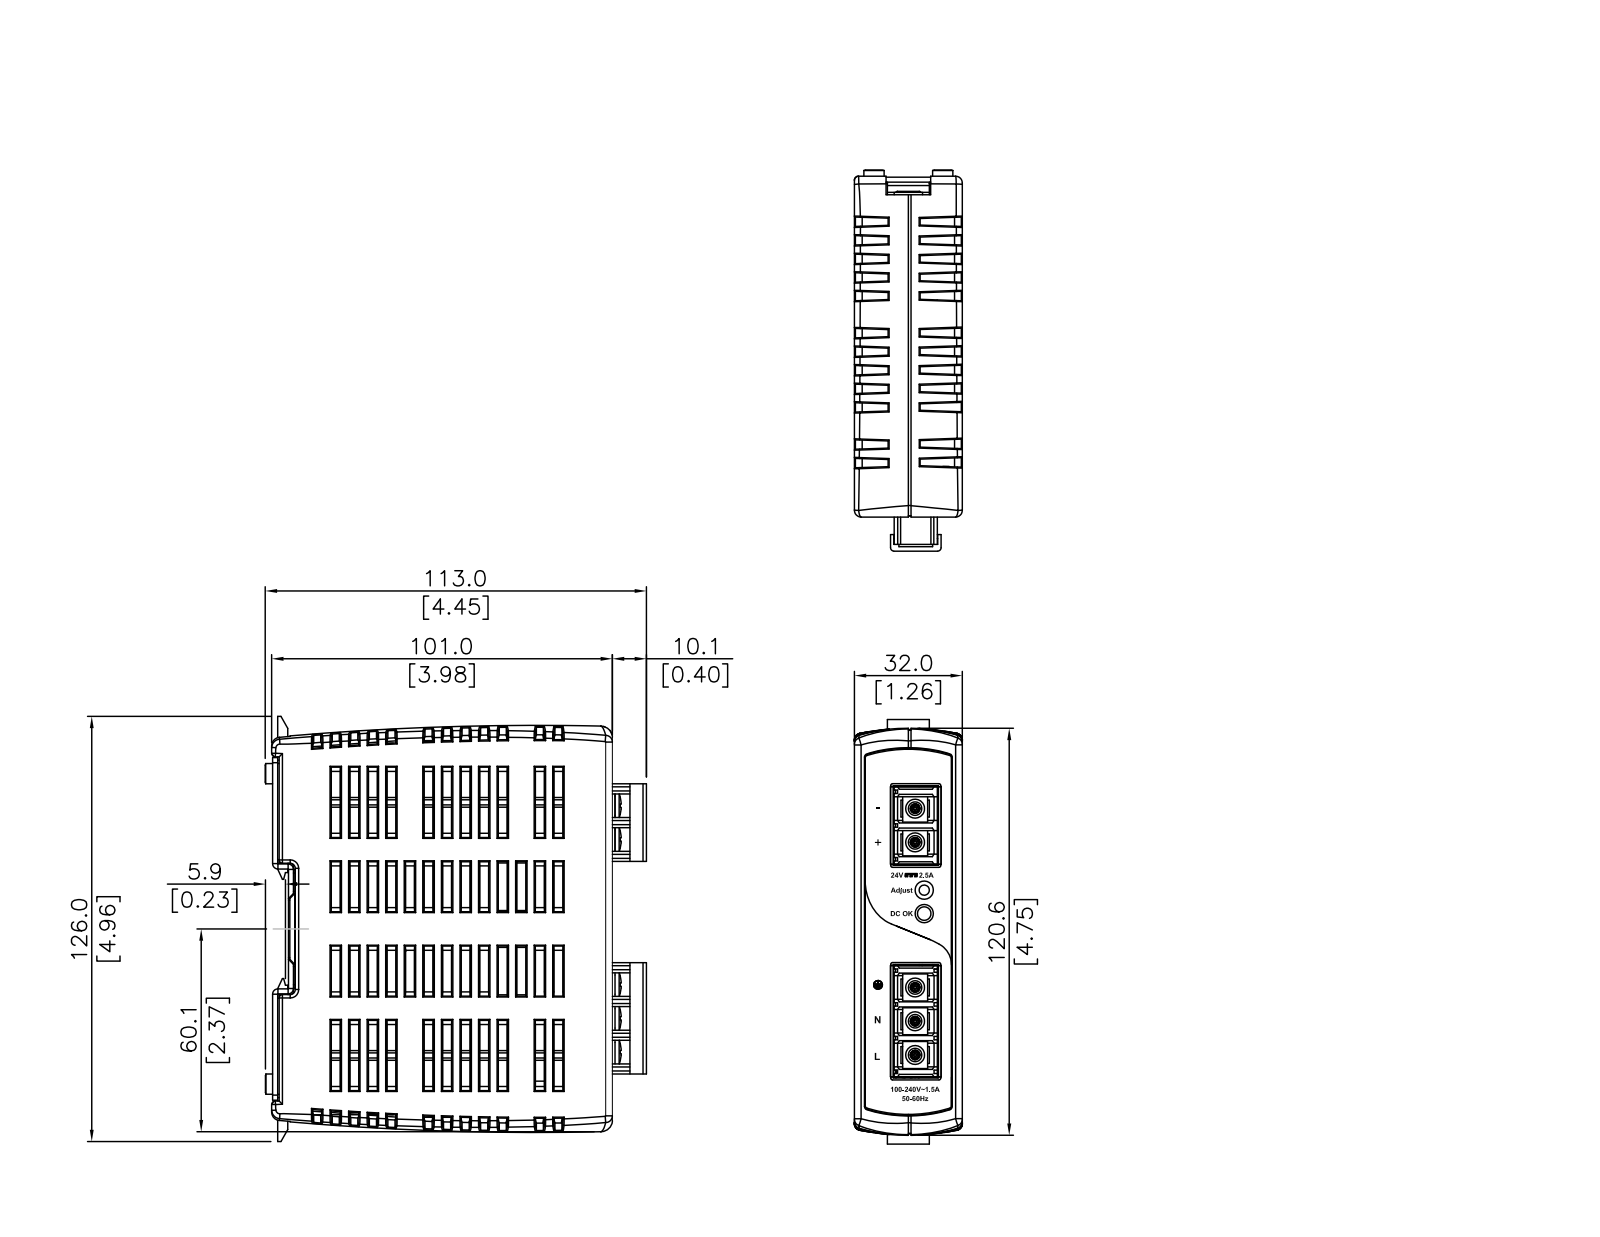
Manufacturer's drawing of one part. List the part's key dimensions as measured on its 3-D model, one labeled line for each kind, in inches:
Part name (STEP PRODUCT): PSB24-060-P.
STEP written by: SolidWorks 2011 (CONFIG_CONTROL_DESIGN)
Units: inches
Bodies: 1 solid, 1354 faces (1032 planar, 74 cylindrical, 248 other)
Overall size (bounding box): 4.98 × 4.398 × 1.26
Volume: 16.01 in³ · Surface area: 120.4 in²
Round holes (diameter × count): ⌀0.175 ×2
Round bosses / shafts (diameter × count): ⌀0.202 ×5, ⌀0.21 ×4, ⌀0.094 ×1
Partial cylindrical surfaces — rounded edges, fillets, slot ends (radius × count): R0.06 ×26, R0.03 ×4, R0.105 ×2, R2.14 ×1
Main face-to-face distances: 0.08, 1.26, 0.37, 0.89, 1.18, 0.29, 0.4, 0.799, 1.199, 0.17
Hole centre spacings: 0.3
